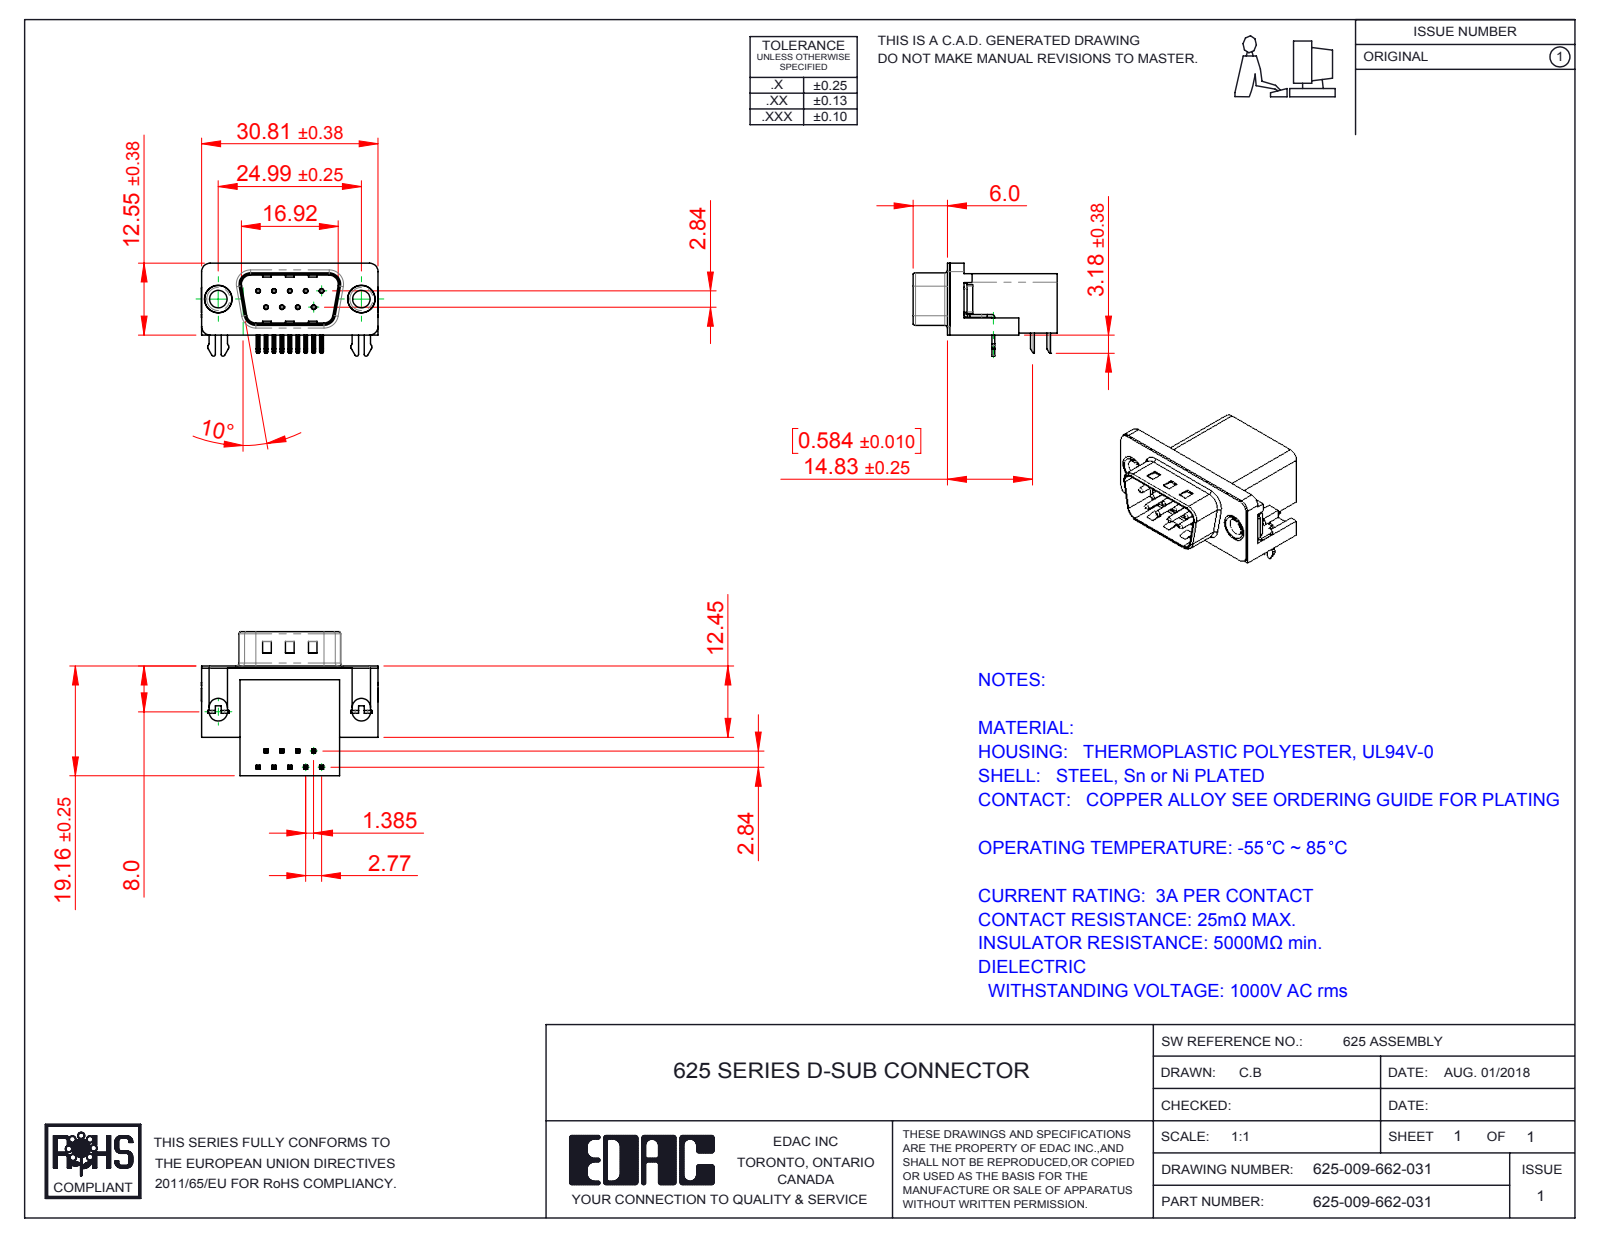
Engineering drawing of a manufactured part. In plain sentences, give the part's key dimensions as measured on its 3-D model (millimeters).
The part is named "625 Housing_9 Socket; 625-009-662-031; 625 Shell_9 Socket; 625 Contact Top (+3 more)". Its 3-D file was written by "SolidWorks 2016 (CONFIG_CONTROL_DESIGN)". It is 15 solids with 993 faces: 605 planar, 307 cylindrical and 81 other. Overall it measures 30.89 by 25.16 by 16.25 millimeters. Its volume is 4 462 cubic millimeters and its surface area 4 934 square millimeters. Round holes: 9 of diameter 0.35, 9 of diameter 0.8, 2 of diameter 3.05, 2 of diameter 4, 2 of diameter 4.8, 2 of diameter 5. Round bosses or shafts: 9 of diameter 0.75, 2 of diameter 4.9, 2 of diameter 4.75, 2 of diameter 3.85. Partial cylindrical surfaces (rounded edges, fillets, slot ends): 44 of radius 0.25, 18 of radius 0.12, 16 of radius 1, 14 of radius 0.5, 8 of radius 1.5, 8 of radius 1.6, 4 of radius 0.32, 4 of radius 0.9. The main face-to-face distances are 0.4, 10.34, 18.76, 19.16, 16.26, 2.5, 2.9, 0.35, 10.69, 0.5. The hole center spacings are 3.16, 2.77, 5.54, 5.03, 5.04, 8.31, 7.48, 7.49.
